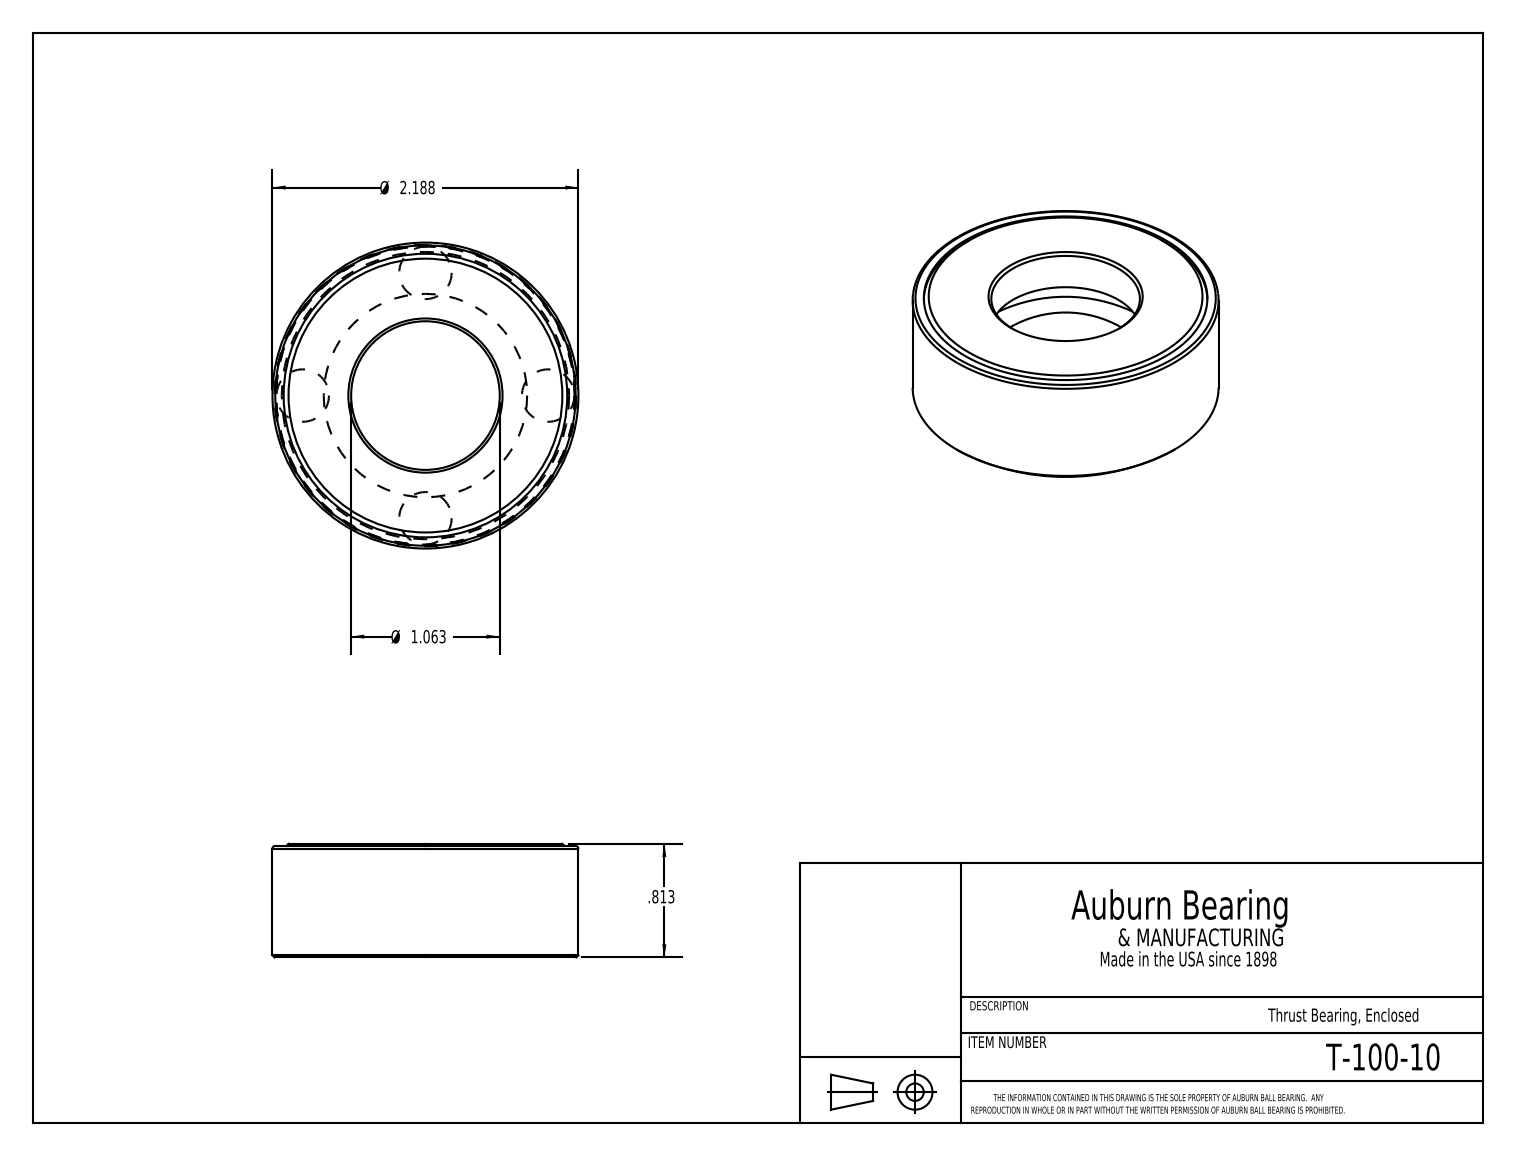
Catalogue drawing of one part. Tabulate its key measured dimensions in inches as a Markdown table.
| quantity | value |
| --- | --- |
| part name | T-100-10 |
| STEP written by | SolidWorks 2016 (CONFIG_CONTROL_DESIGN) |
| units | inches |
| bodies | 6 solids, 28 faces (9 planar, 7 cylindrical, 12 other) |
| overall size | 2.188 × 2.188 × 0.813 |
| volume | 1.619 in³ |
| surface area | 26.5 in² |
| round holes (diameter × count) | 1.063 × 1, 2.027 × 1, 2.147 × 1 |
| round bosses / shafts (diameter × count) | 2.187 × 1, 2.133 × 1 |
| main face-to-face distances | 0.294, 0.519, 0.813, 0.225, 0.798, 0.504, 0.279, 0.015, 0.778, 0.484 |
